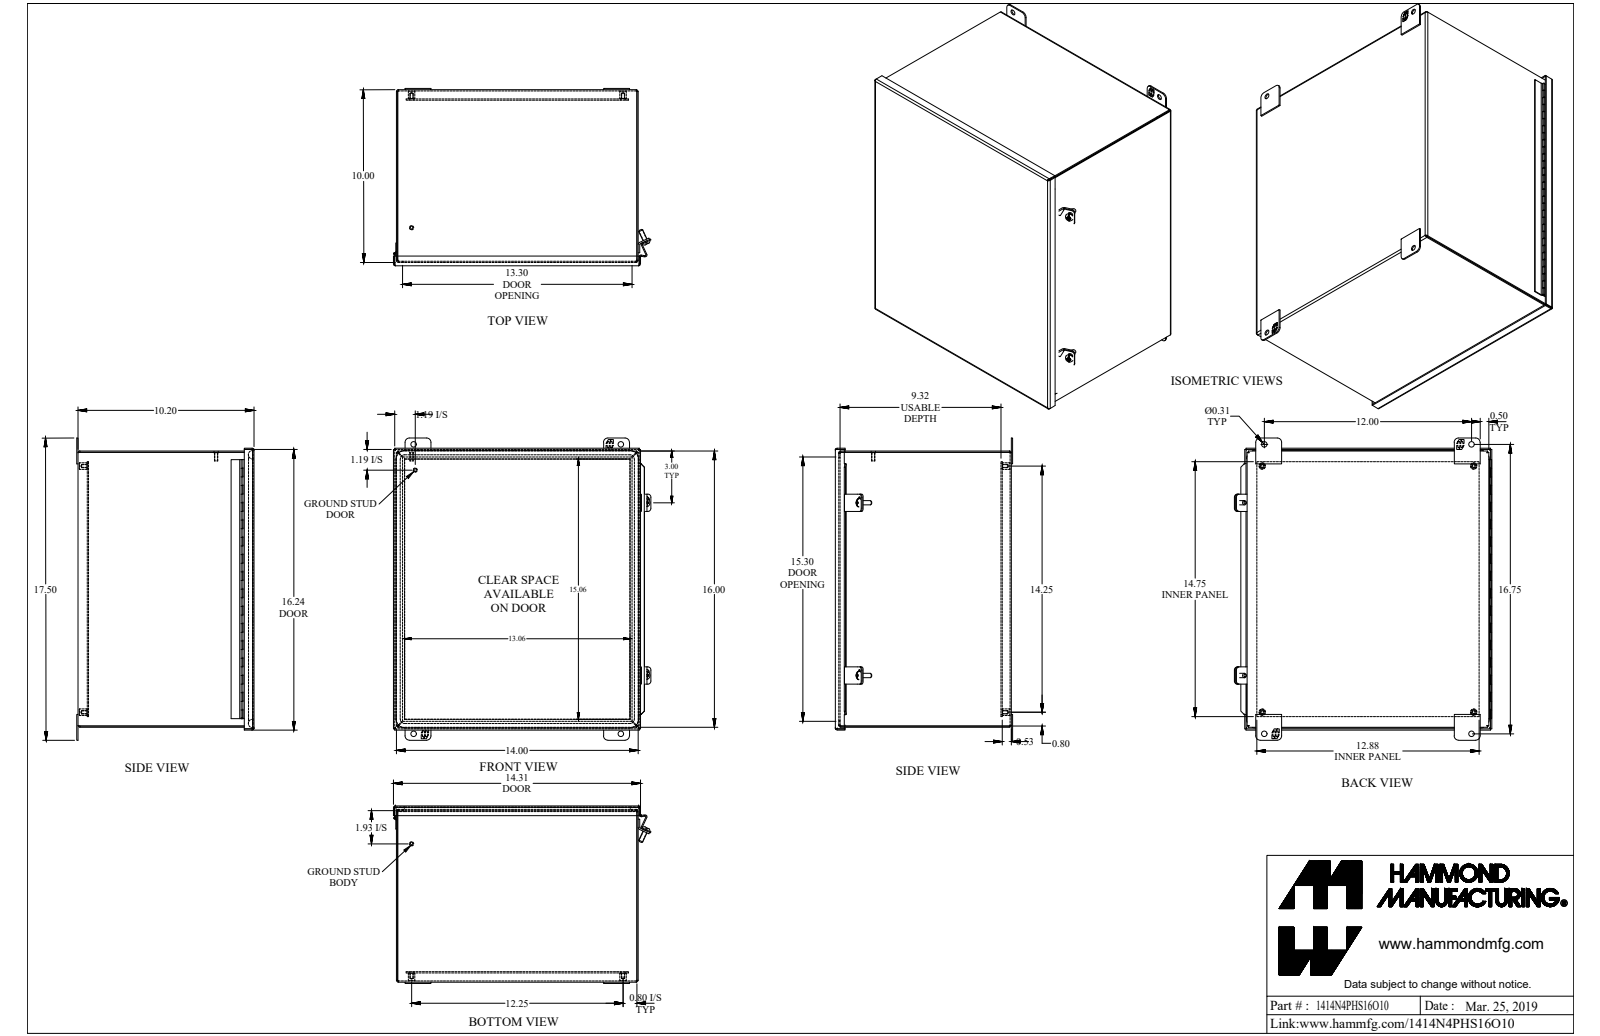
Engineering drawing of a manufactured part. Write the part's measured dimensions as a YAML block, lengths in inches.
part_name: "1414N4PHS16O10"
step_written_by: "SolidWorks 2018 (AUTOMOTIVE_DESIGN)"
units: inches
bodies: {solids: 21, faces: 778, planar: 496, cylindrical: 220, other: 62}
overall_size: [17.5, 14.903, 10.269]
volume: 99.93
surface_area: 2797
round_holes:
  - {diameter: 0.156, count: 4}
  - {diameter: 0.265, count: 4}
  - {diameter: 0.313, count: 4}
  - {diameter: 0.213, count: 2}
  - {diameter: 0.05, count: 1}
round_bosses_or_shafts:
  - {diameter: 0.375, count: 4}
  - {diameter: 0.25, count: 4}
  - {diameter: 0.48, count: 2}
  - {diameter: 0.19, count: 2}
  - {diameter: 0.1, count: 1}
  - {diameter: 0.045, count: 1}
partial_cylinders:
  - {radius: 0.25, count: 24}
  - {radius: 0.036, count: 9}
  - {radius: 0.108, count: 9}
  - {radius: 0.188, count: 8}
  - {radius: 0.007, count: 4}
  - {radius: 0.046, count: 4}
  - {radius: 0.079, count: 4}
  - {radius: 0.118, count: 4}
face_to_face_distances: [0.072, 10.125, 9.593, 0.532, 13.928, 15.928, 10.197, 10.053, 0.604, 9.665]
hole_center_spacings: [12.189, 12.25, 19.679, 1.256, 15.5, 1.257, 12, 14.25]
